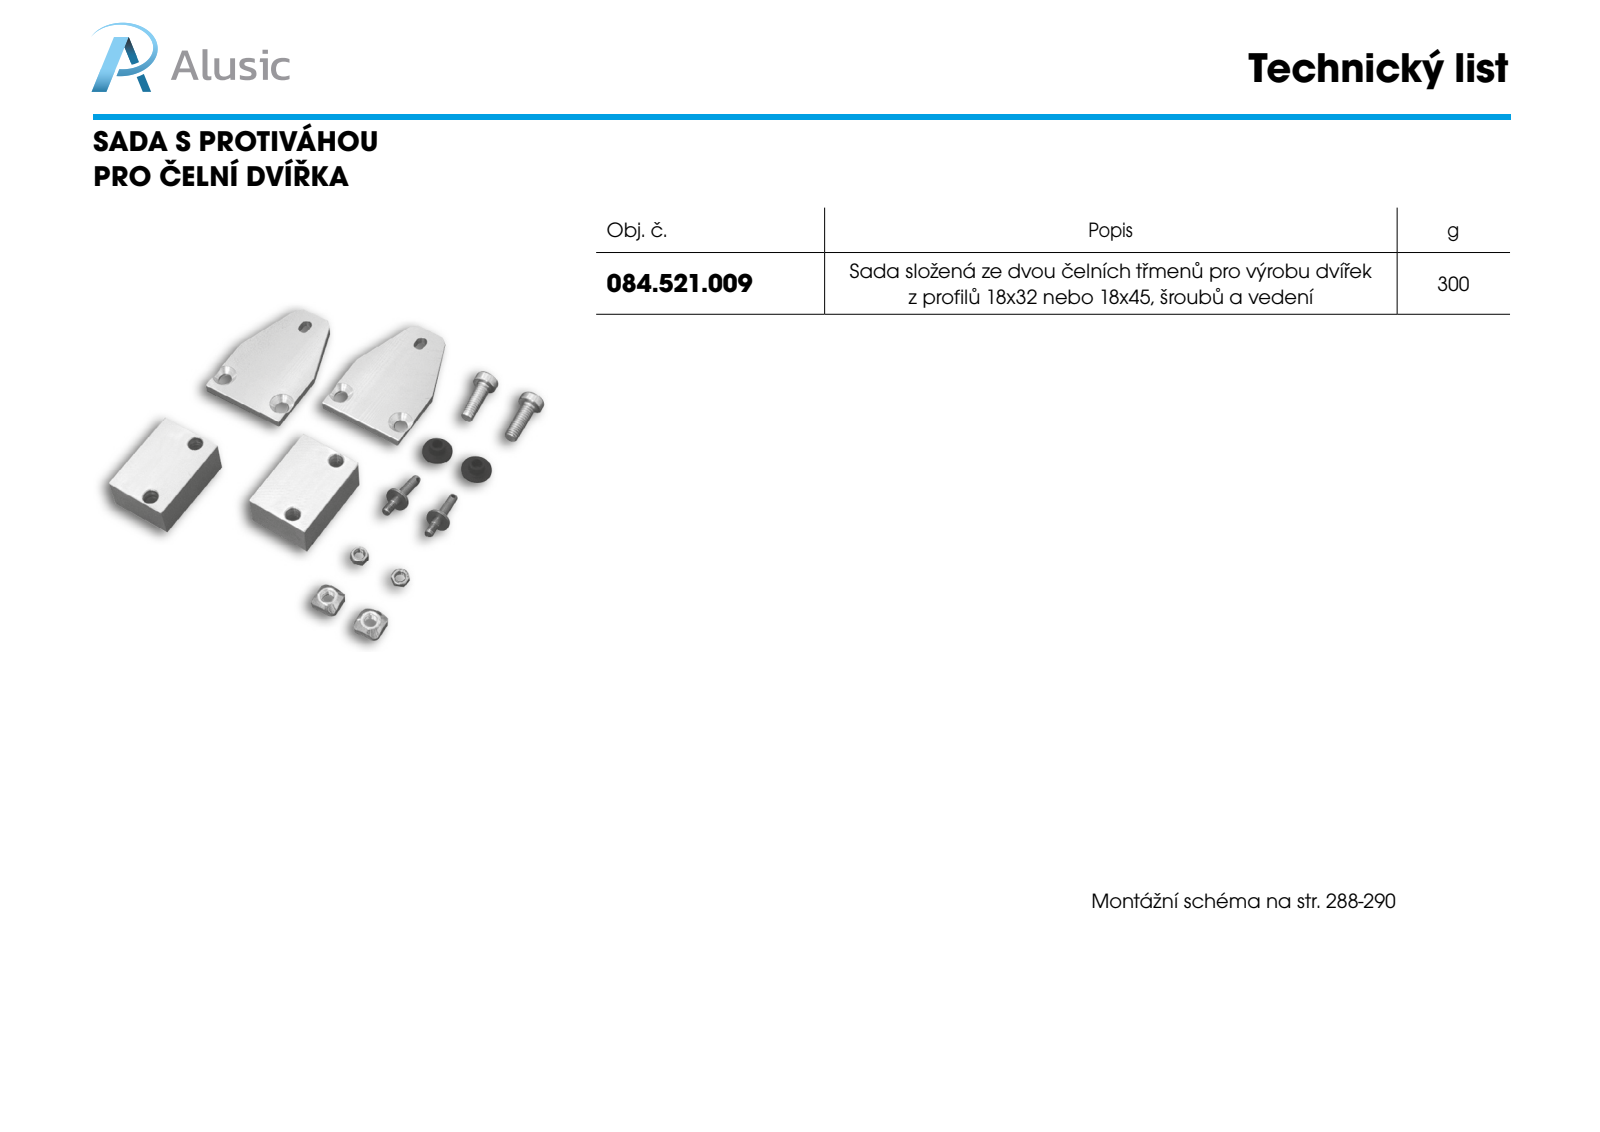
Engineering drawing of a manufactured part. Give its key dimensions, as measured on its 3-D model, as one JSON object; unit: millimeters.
{"part_name": "084.521.108; 084.521.109_Default<A macchina>; 084.521.009; ISO 10642 - M6 x 30 --- 30S_ISO 10642 - M6 x 30 --- 30S (+3 more)", "step_written_by": "SolidWorks 2016 (CONFIG_CONTROL_DESIGN)", "units": "millimeters", "bodies": {"solids": 7, "faces": 458, "planar": 58, "cylindrical": 146, "other": 254}, "overall_size": [68.25, 45, 35], "volume_mm3": 39594, "surface_area_mm2": 16148, "round_holes": [[6.5, 2], [7, 2], [2, 1], [4.2, 1], [5.1, 1]], "round_bosses_or_shafts": [[11.34, 2], [6, 2], [15, 1], [12, 1], [8, 1], [5, 1], [4.5, 1]], "partial_cylinders_radius": [[2.75, 2], [5, 1], [15, 1]], "face_to_face_distances": [5, 18, 23, 32, 45, 1.5, 6.5, 16.5, 8, 15], "hole_center_spacings": [52.92, 30]}
